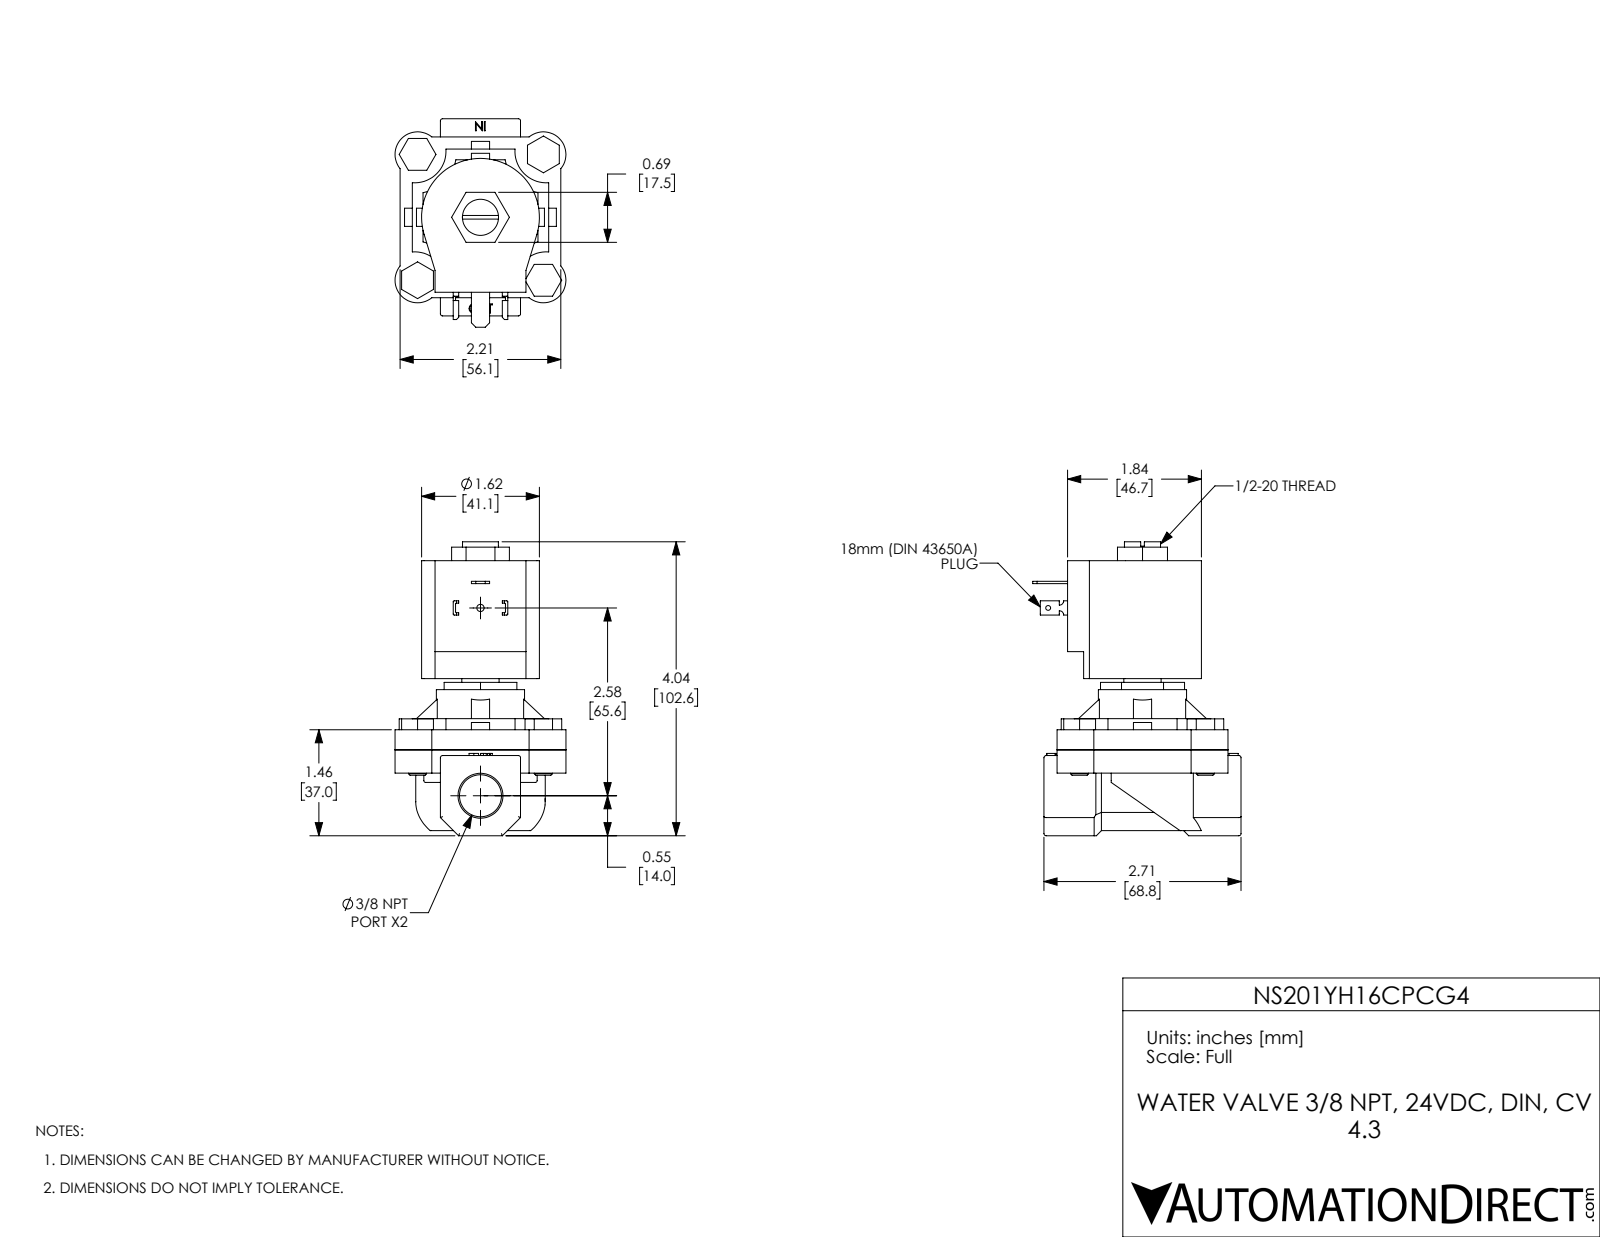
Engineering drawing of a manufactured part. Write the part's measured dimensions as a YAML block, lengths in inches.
part_name: "NS201YH16CPCG4"
step_written_by: "SolidWorks 2024 (CONFIG_CONTROL_DESIGN)"
units: inches
bodies: {solids: 11, faces: 383, planar: 237, cylindrical: 113, other: 33}
overall_size: [4.04, 2.865, 2.35]
volume: 10.3
surface_area: 66.77
round_holes:
  - {diameter: 0.25, count: 4}
  - {diameter: 0.067, count: 1}
  - {diameter: 0.1, count: 1}
  - {diameter: 0.496, count: 1}
  - {diameter: 0.512, count: 1}
  - {diameter: 0.578, count: 1}
  - {diameter: 1.155, count: 1}
round_bosses_or_shafts:
  - {diameter: 0.248, count: 4}
  - {diameter: 1.213, count: 1}
partial_cylinders:
  - {radius: 0.03, count: 15}
  - {radius: 0.015, count: 8}
  - {radius: 0.31, count: 4}
  - {radius: 0.432, count: 4}
  - {radius: 0.579, count: 4}
  - {radius: 0.06, count: 2}
  - {radius: 0.81, count: 1}
  - {radius: 0.89, count: 1}
face_to_face_distances: [0.276, 2.599, 2.323, 0.32, 0.596, 2.919, 0.554, 1.656, 0.25, 2.46]
hole_center_spacings: [1.223, 1.73, 2.446, 2.581]
